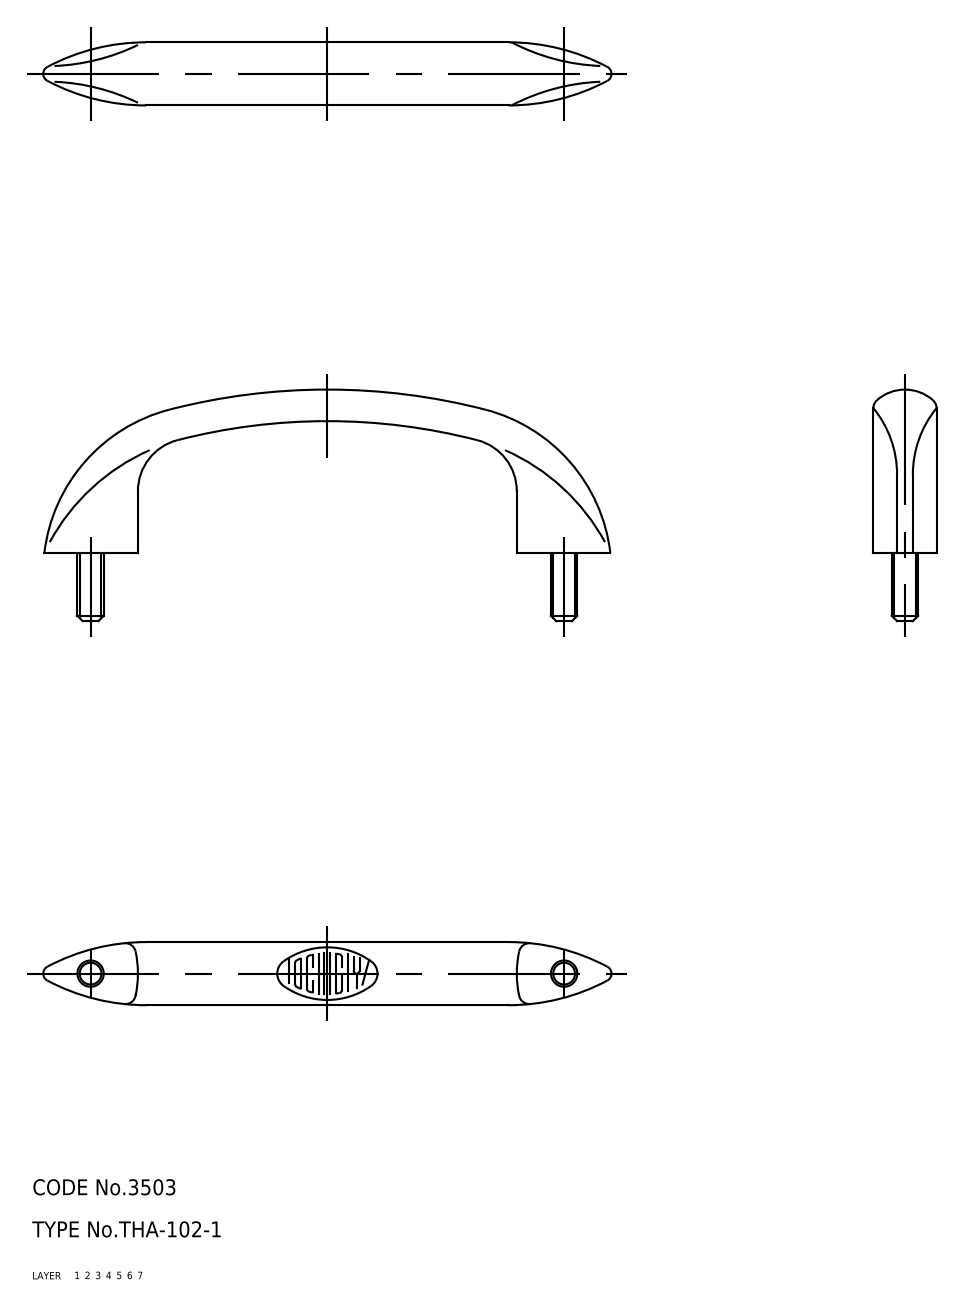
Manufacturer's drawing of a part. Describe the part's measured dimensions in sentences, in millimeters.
The part is named "screw; pull; THA_102_1_26457_36". Its 3-D file was written by "CADfix (AUTOMOTIVE_DESIGN)". It is 3 solids with 22 faces: 0 planar, 0 cylindrical and 22 other. Overall it measures 108 by 44 by 12.04 millimeters. Its volume is 10 225 cubic millimeters and its surface area 5 457 square millimeters.
